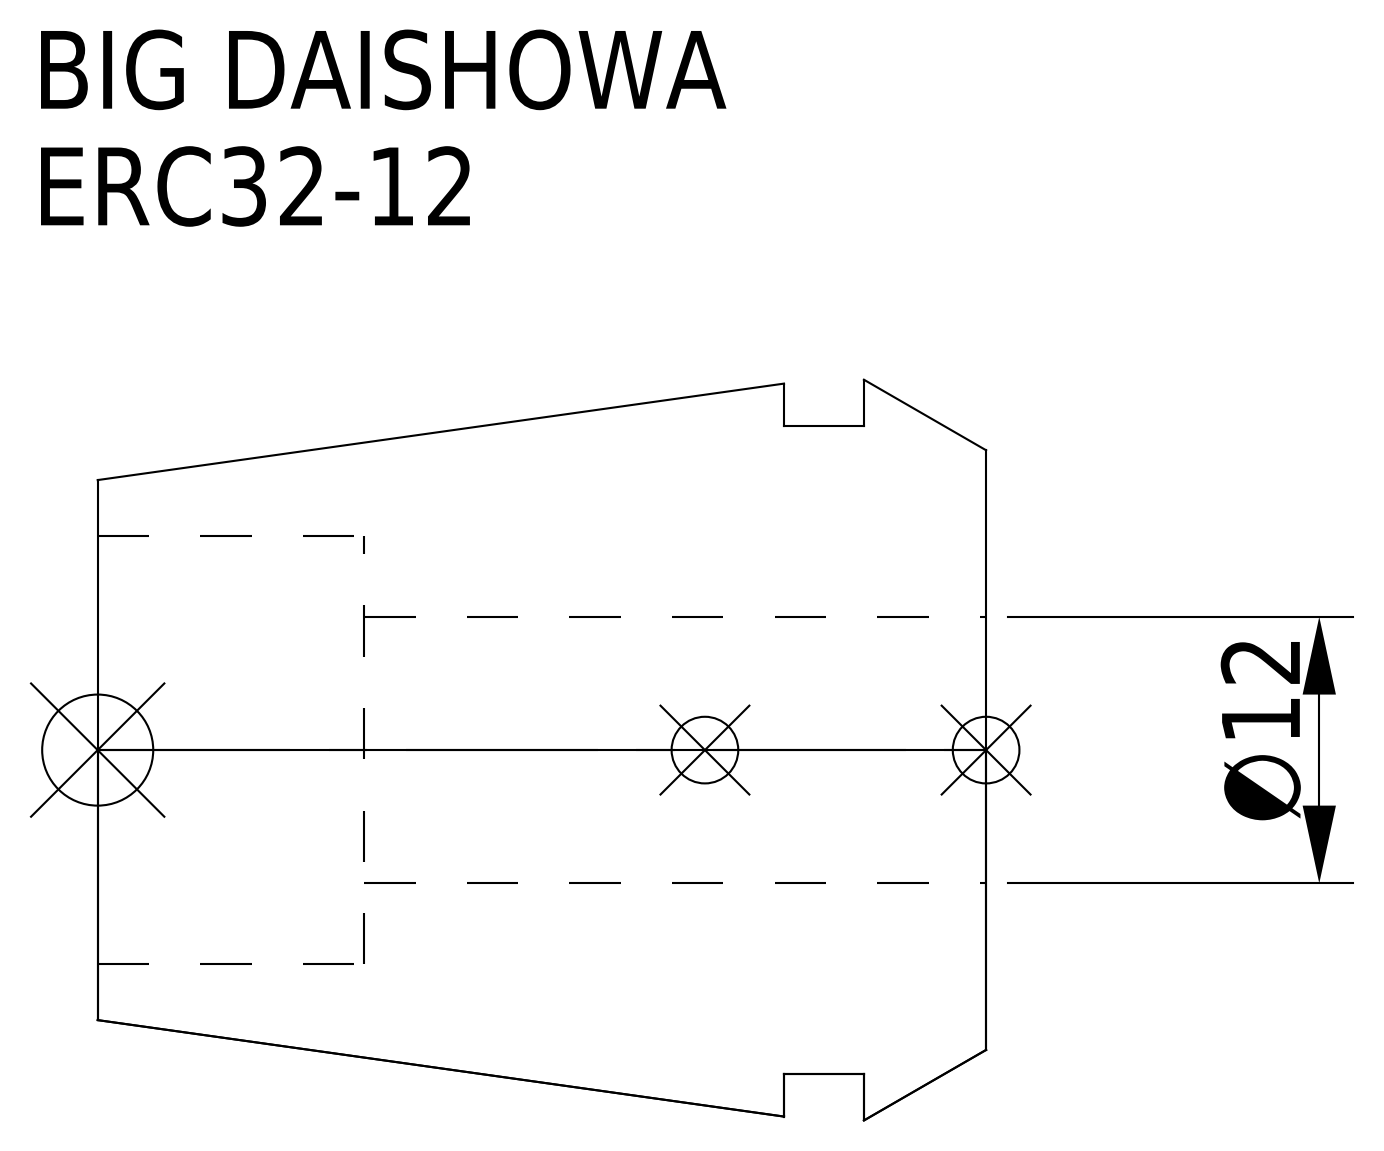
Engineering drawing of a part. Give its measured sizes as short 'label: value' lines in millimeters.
name: ERC32-12
written by: CREO PARAMETRIC BY PTC INC, 2016380 (AUTOMOTIVE_DESIGN)
unit: mm
bodies: 1 solid, 15 faces (5 planar, 6 cylindrical, 4 other)
size: 40 × 33.35 × 33.35
volume: 19 765 mm³; area: 6 725 mm²
holes: 1× ⌀12, 1× ⌀19.3
bosses: 1× ⌀29.2
face distances: 5.5, 9.1, 3.6, 28, 22.5, 18.9, 40, 34.5, 30.9, 12
